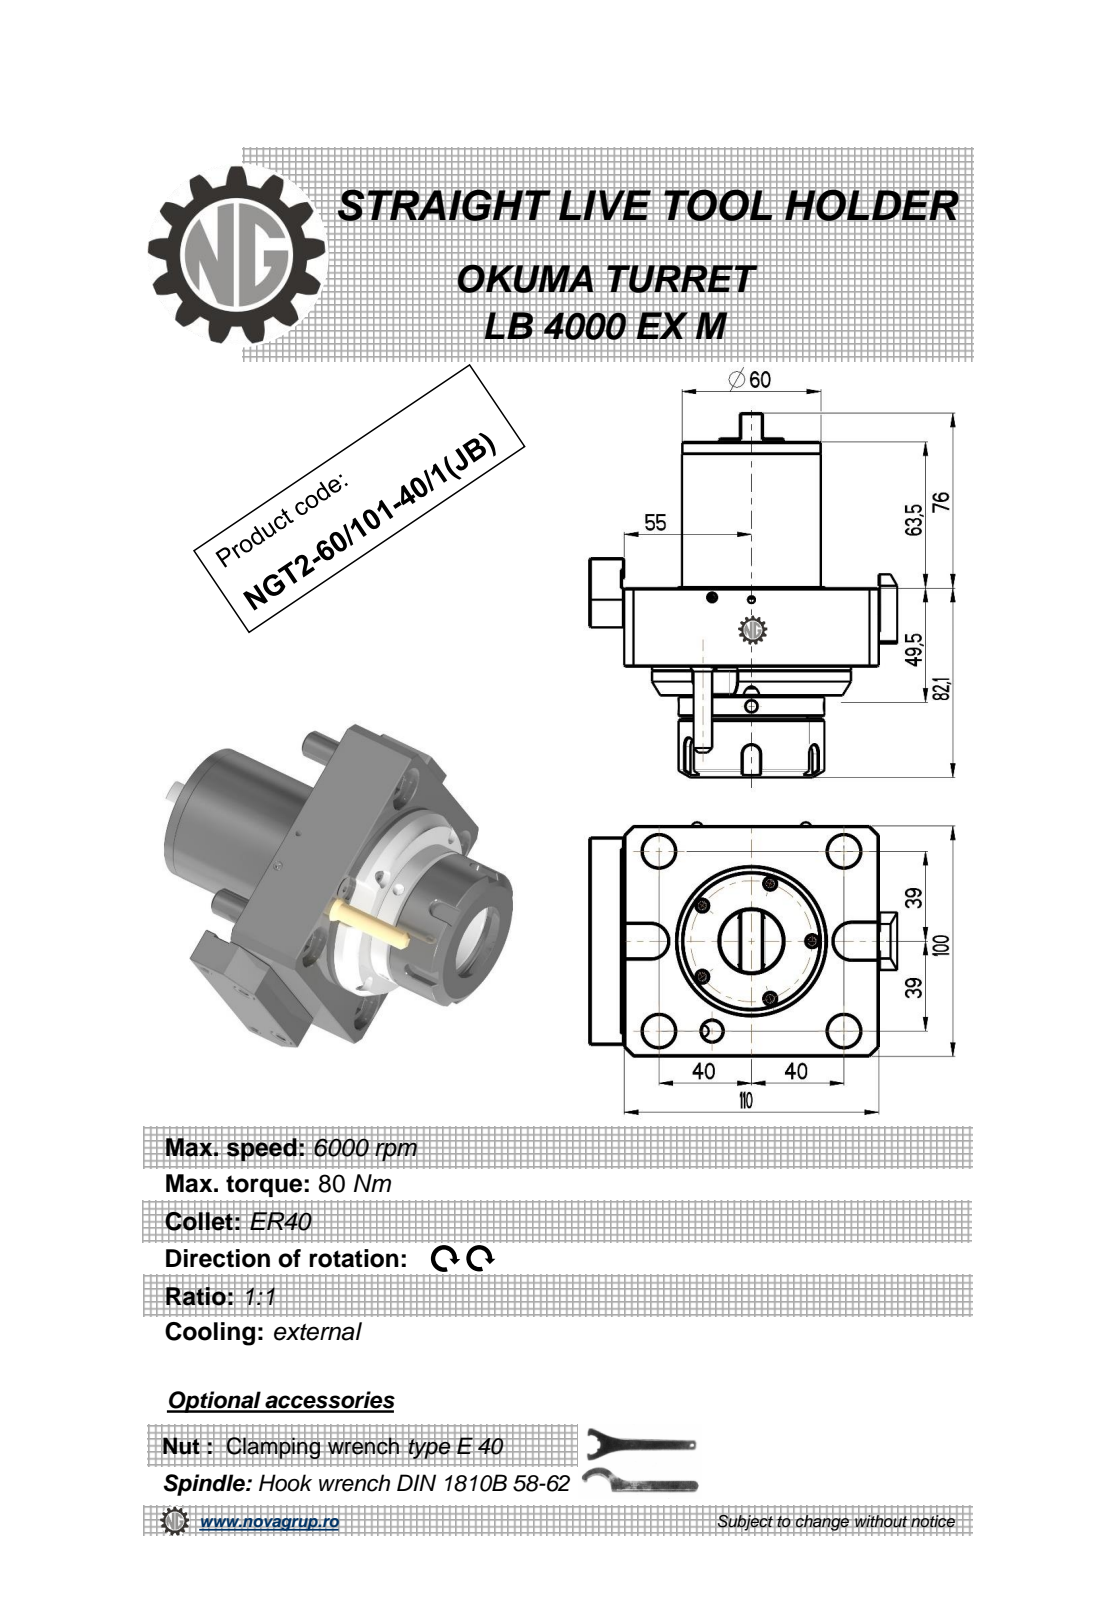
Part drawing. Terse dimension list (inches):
name: NGT2_60_101_40_1_JB
written by: PRO/ENGINEER BY PARAMETRIC TECHNOLOGY CORPORATION, 2010280 (CONFIG_CONTROL_DESIGN)
unit: in
bodies: 1 solid, 350 faces (166 planar, 88 cylindrical, 96 other)
size: 6.224 × 5.236 × 3.937
volume: 47.16 in³; area: 118.9 in²
holes: 5× ⌀0.197, 1× ⌀0.118, 1× ⌀0.13, 1× ⌀0.354, 1× ⌀1.319
bosses: 4× ⌀0.472, 3× ⌀0.236, 1× ⌀3.386, 1× ⌀2.48, 1× ⌀2.362, 1× ⌀2.008, 1× ⌀1.102, 1× ⌀0.441
rounds: 10× R0.012, 6× R0.009, 5× R0.148, 2× R0.031, 2× R0.236, 1× R0.197, 1× R0.295, 1× R0.315
face distances: 1.339, 4.331, 3.937, 0.492, 1.831, 1.85, 4.921, 2.5, 3.839, 0.512
hole spacings: 2.717, 0.157, 1.675, 1.744, 1.977, 2.913
